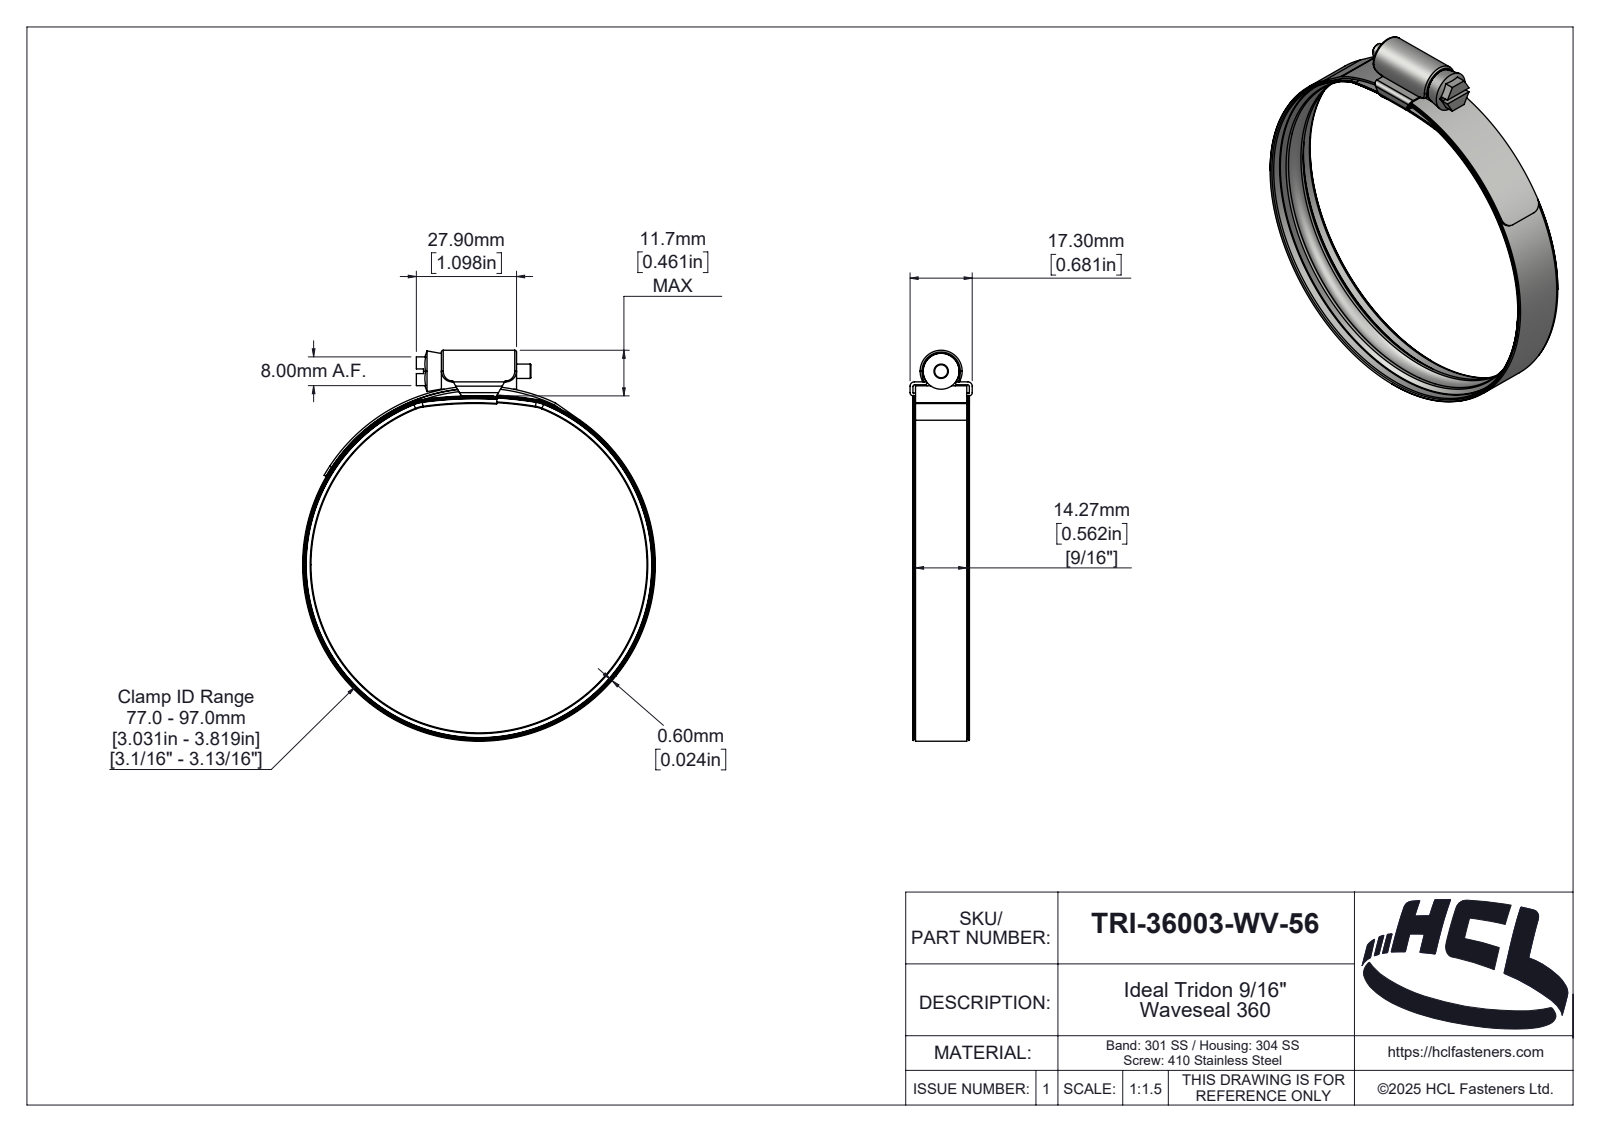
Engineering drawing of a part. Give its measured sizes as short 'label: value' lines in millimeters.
name: TRI-36003-WV-56
written by: SolidWorks 2025 (AUTOMOTIVE_DESIGN)
unit: mm
bodies: 4 solids, 418 faces (42 planar, 119 cylindrical, 257 other)
size: 108.8 × 98.2 × 17.3
volume: 7 015 mm³; area: 24 553 mm²
holes: 1× ⌀96.4, 1× ⌀97
bosses: 1× ⌀98.2, 1× ⌀96.8, 1× ⌀10, 1× ⌀4
rounds: 6× R0.5, 4× R3, 2× R0.1, 2× R0.9, 2× R1.2, 2× R9.9, 2× R10.1, 1× R0.46
face distances: 0.8, 14.26, 3.1, 0.6, 2.3, 3.9, 27.9, 1.52, 15.78, 16.5
